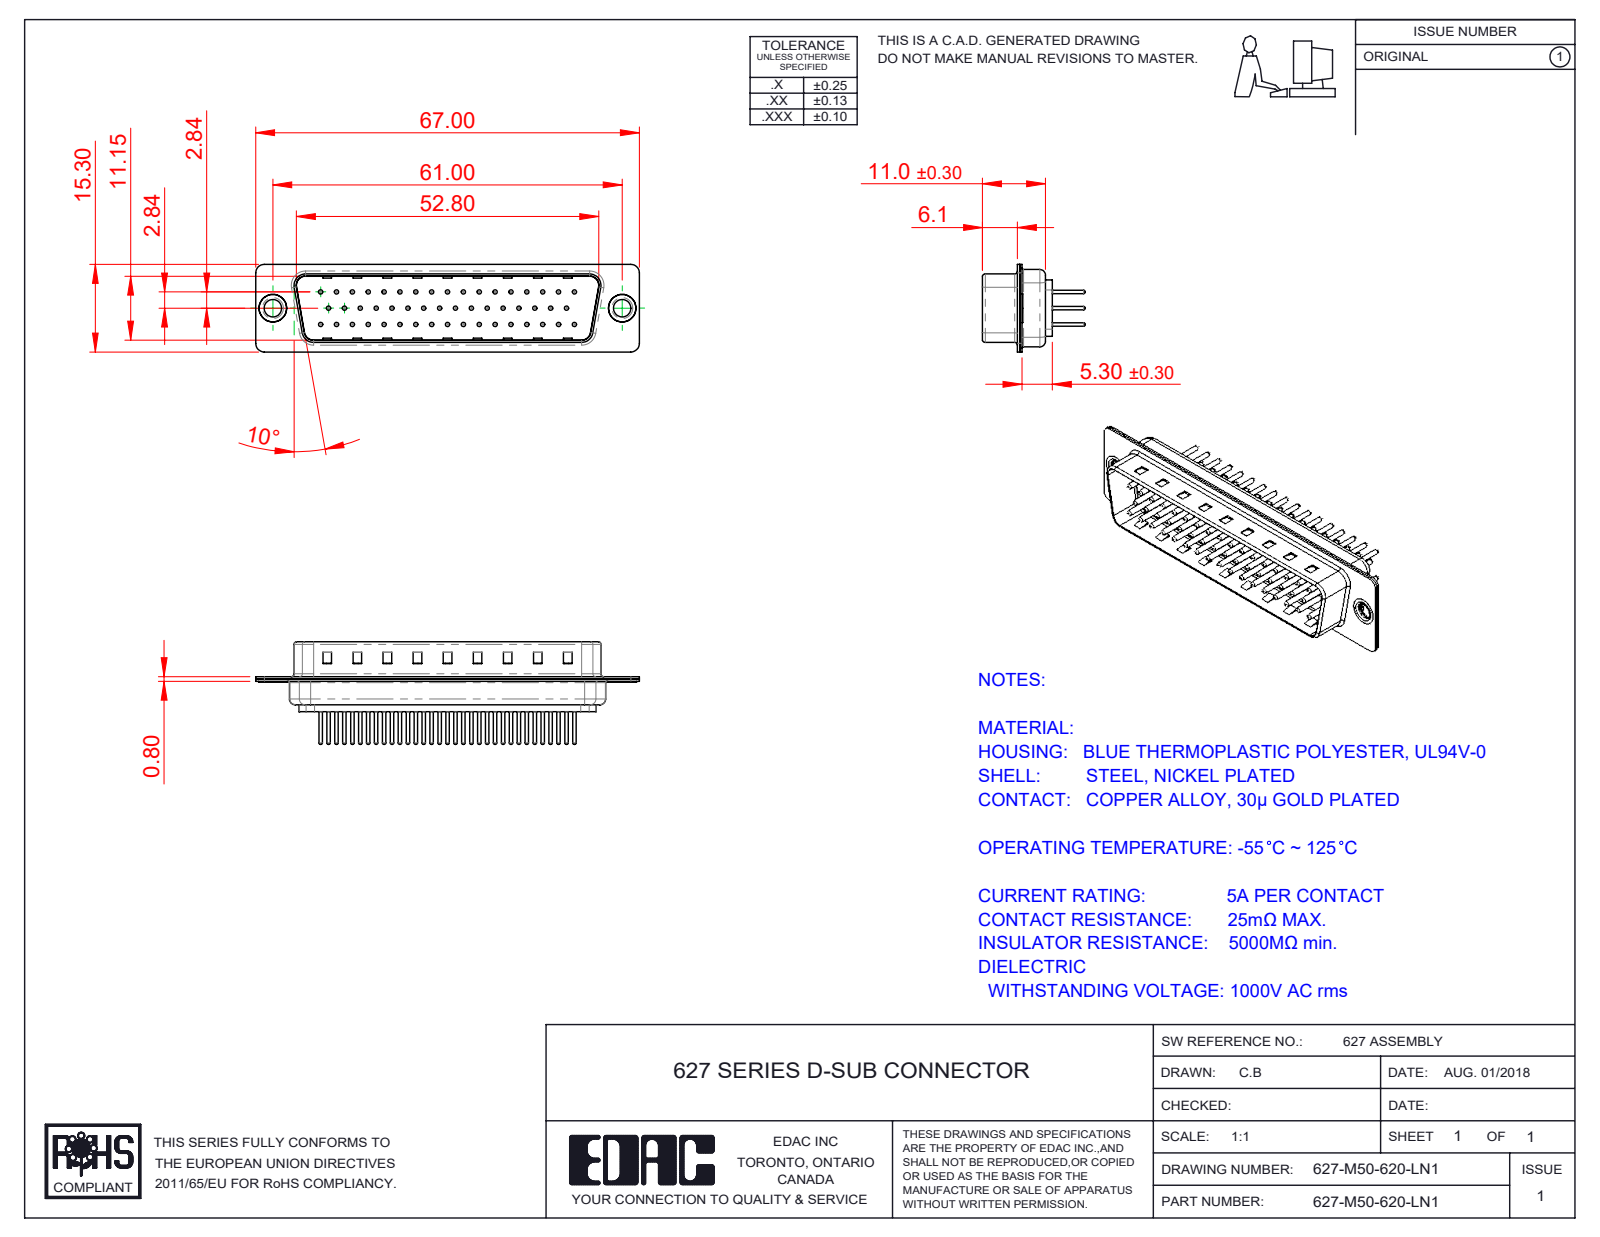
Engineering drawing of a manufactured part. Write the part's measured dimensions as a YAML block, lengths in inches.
part_name: "627M Contact Row 1_20; 627-M50-620-LN1; 627M Shell Front_50 Contacts; 627M Thru Hole Rivet (+4 more)"
step_written_by: "SolidWorks 2020 (CONFIG_CONTROL_DESIGN)"
units: inches
bodies: {solids: 55, faces: 2236, planar: 553, cylindrical: 825, other: 858}
overall_size: [2.638, 0.705, 0.602]
volume: 0.271
surface_area: 16.36
round_holes:
  - {diameter: 0.03, count: 50}
  - {diameter: 0.063, count: 50}
  - {diameter: 0.079, count: 50}
  - {diameter: 0.12, count: 2}
  - {diameter: 0.157, count: 2}
  - {diameter: 0.189, count: 2}
round_bosses_or_shafts:
  - {diameter: 0.059, count: 50}
  - {diameter: 0.024, count: 50}
  - {diameter: 0.197, count: 2}
  - {diameter: 0.193, count: 2}
  - {diameter: 0.14, count: 2}
partial_cylinders:
  - {radius: 0.059, count: 16}
  - {radius: 0.079, count: 12}
  - {radius: 0.02, count: 8}
  - {radius: 0.063, count: 8}
  - {radius: 0.01, count: 4}
  - {radius: 0.024, count: 4}
  - {radius: 0.026, count: 4}
  - {radius: 0.035, count: 4}
face_to_face_distances: [0.016, 0.455, 0.224, 0.24, 0.031, 0.03, 0.485, 0.485, 0.516, 0.209]
hole_center_spacings: [0.124, 0.109, 0.218, 0.327, 0.436, 0.545, 0.654, 0.198]
